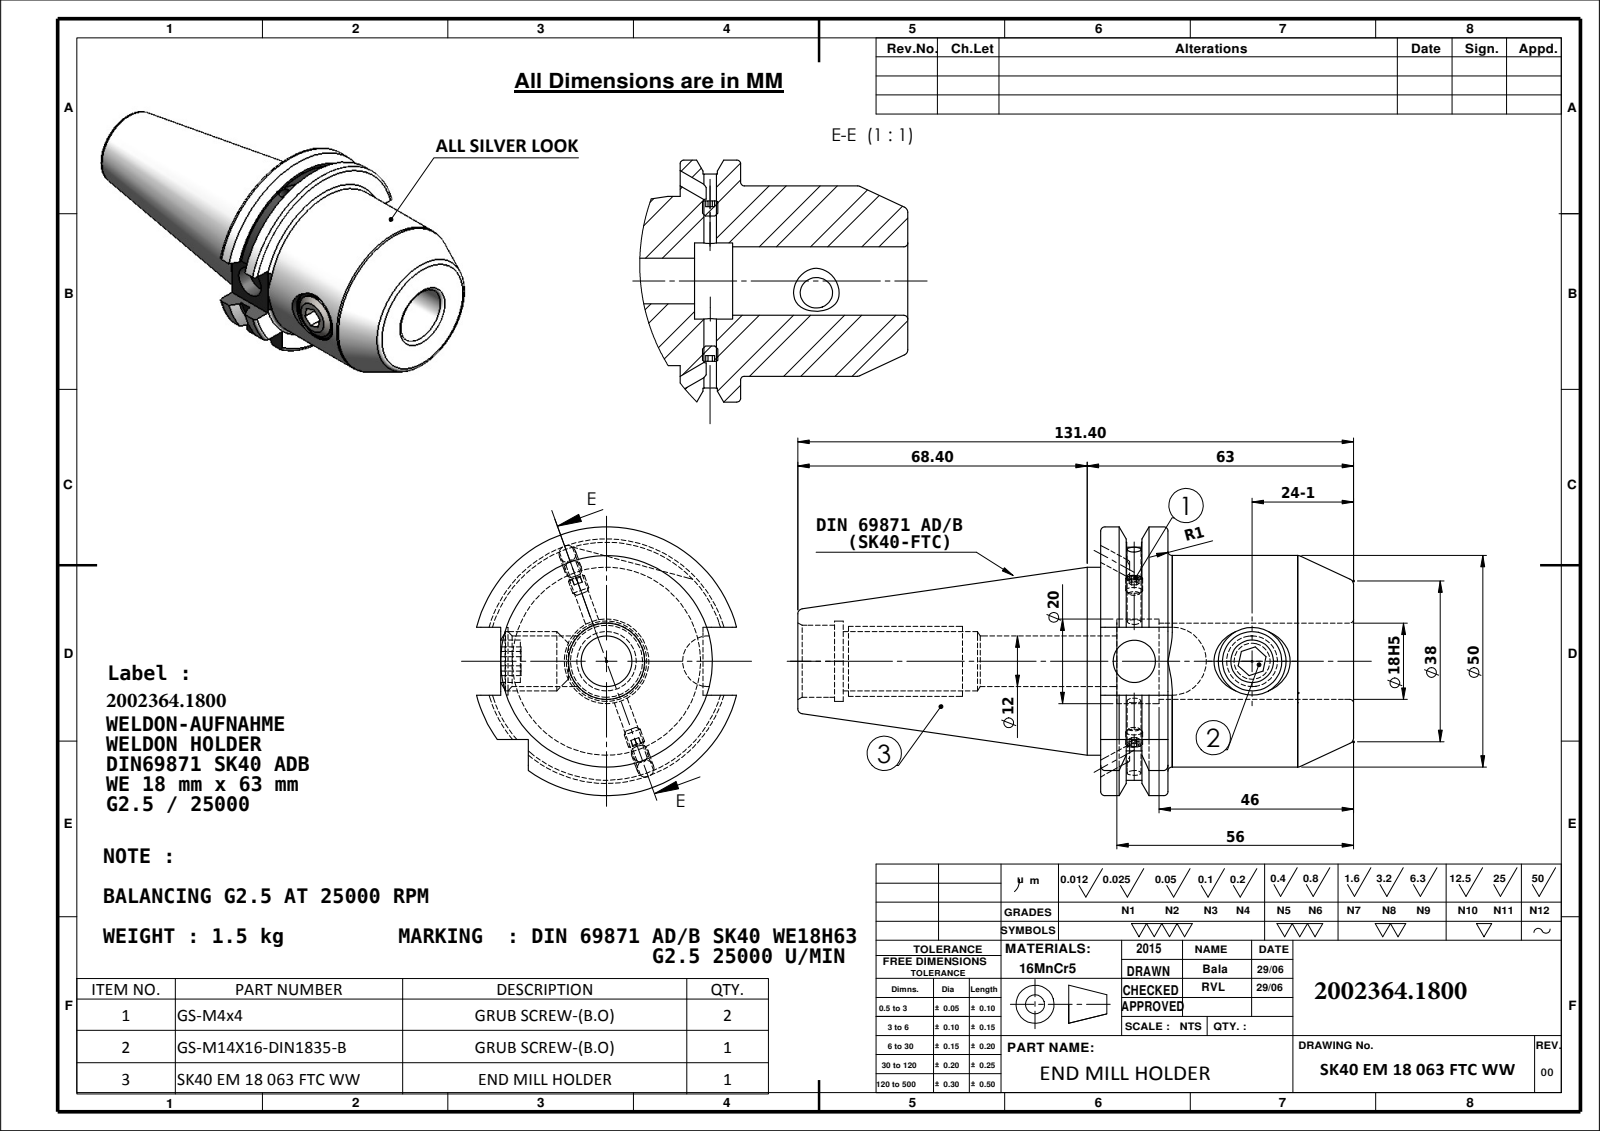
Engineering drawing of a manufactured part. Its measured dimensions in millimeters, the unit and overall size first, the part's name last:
Units: millimetres
Overall size (bounding box): 131.4 × 63.55 × 61.48
Round holes (diameter × count): ⌀12 ×2, ⌀3.3 ×1, ⌀10 ×1, ⌀14 ×1, ⌀16 ×1, ⌀17 ×1, ⌀18 ×1, ⌀19 ×1, ⌀20 ×1
Round bosses / shafts (diameter × count): ⌀4 ×2, ⌀50 ×1, ⌀44.45 ×1, ⌀14 ×1
Partial cylindrical surfaces — rounded edges, fillets, slot ends (radius × count): R8.05 ×1, R28.12 ×1, R31.77 ×1
Main face-to-face distances: 59.8, 15.9, 43.9, 47.8, 3.8, 12.1, 56, 16.1, 71.6, 75.4
Hole centre spacings: 27.85
Volume: 166 778 mm³ · Surface area: 31 492 mm²
Bodies: 4 solids, 163 faces (59 planar, 45 cylindrical, 59 other)
Part name (STEP PRODUCT): SK40 EM 18 063 FTC WW; Copy of M4X4_DIN 913 - M4 x 4-N; M14X16_ISO 4026 - M12 x 12-N; 91406-WE7 18063
STEP written by: SolidWorks 2009 (CONFIG_CONTROL_DESIGN)
